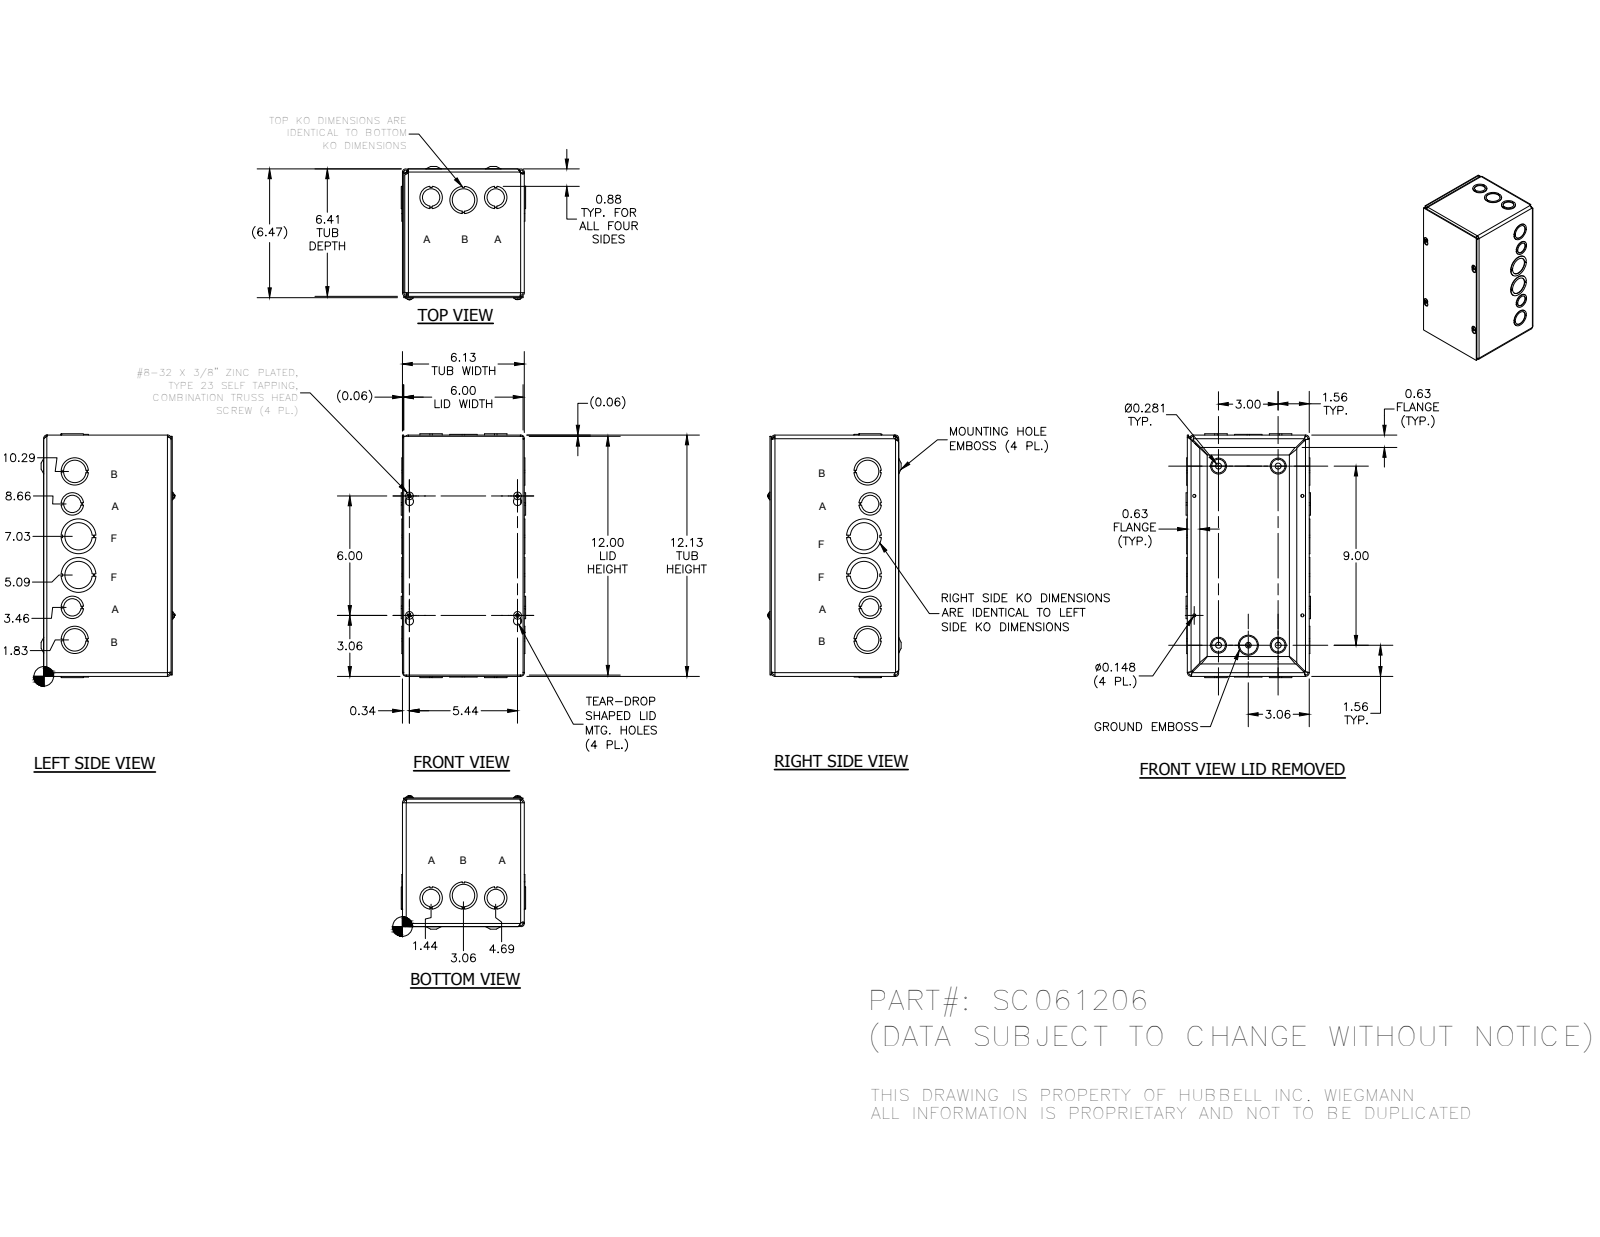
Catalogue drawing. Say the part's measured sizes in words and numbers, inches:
The part is named "SC0612BKP; SC061206WRA; SC0612LID; 34056 (+1 more)". Its 3-D file was written by "Autodesk Inventor 2014 (AUTOMOTIVE_DESIGN)". It is 22 solids with 862 faces: 529 planar, 175 cylindrical and 158 other. Overall it measures 12.249 by 6.693 by 6.249 inches. Round holes: 7 of diameter 1.125, 5 of diameter 1.375, 4 of diameter 0.148, 4 of diameter 0.3, 4 of diameter 0.875, 2 of diameter 1.75, 1 of diameter 0.165. Round bosses or shafts: 4 of diameter 0.384, 4 of diameter 0.164, 1 of diameter 0.228. Partial cylindrical surfaces (rounded edges, fillets, slot ends): 12 of radius 0.125, 8 of radius 0.187, 4 of radius 0.055, 4 of radius 0.062, 4 of radius 0.094, 4 of radius 0.117, 4 of radius 0.124, 4 of radius 0.156. The main face-to-face distances are 0.062, 0.062, 6.343, 6.405, 6.125, 6.063, 6.001, 6.063, 0.063, 6.406. The hole center spacings are 1.933, 7.598, 8.605, 1.5, 1.635, 1.659, 3, 3.265.
